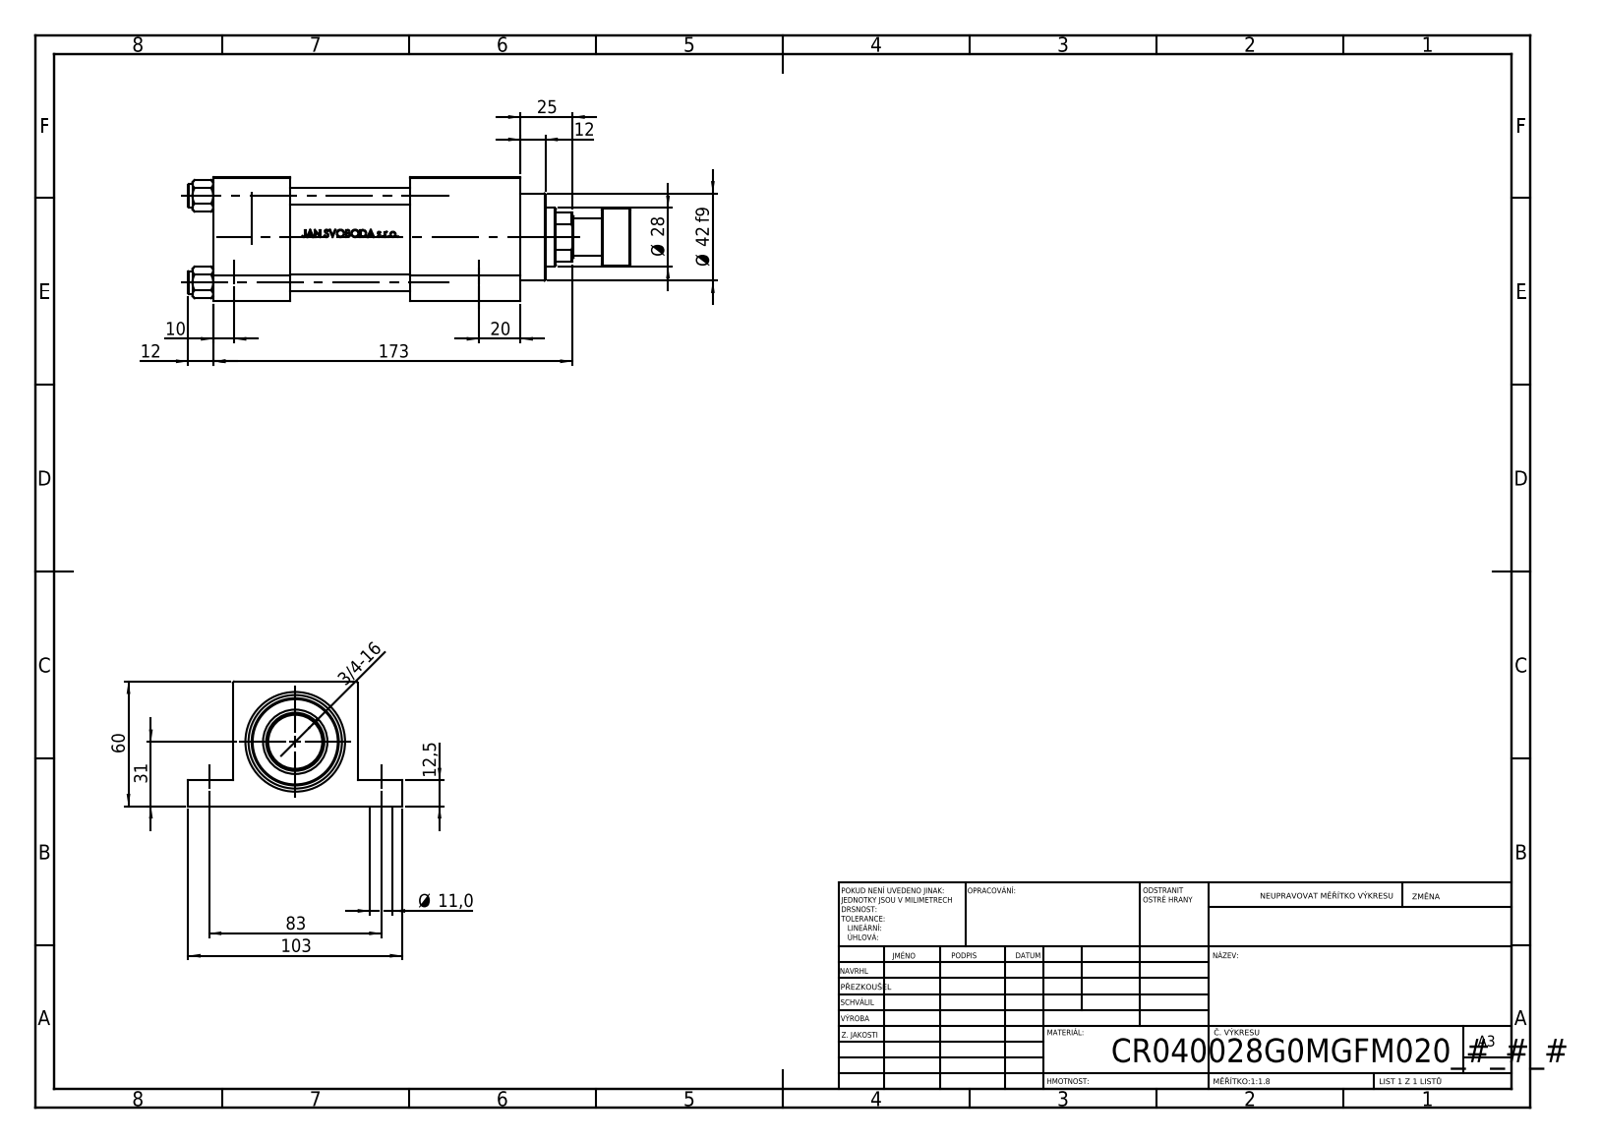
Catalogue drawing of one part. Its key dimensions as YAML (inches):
part_name: "V215CR_G_TYCINKA; V215_VC_A; V215CR_G_Body; V215CR_VCP_G (+2 more)"
step_written_by: "SolidWorks 2019 (CONFIG_CONTROL_DESIGN)"
units: inches
bodies: {solids: 12, faces: 1104, planar: 436, cylindrical: 130, other: 538}
overall_size: [8.386, 4.055, 2.362]
volume: 29.52
surface_area: 191.3
round_holes:
  - {diameter: 0.315, count: 4}
  - {diameter: 0.433, count: 4}
  - {diameter: 0.276, count: 2}
  - {diameter: 0.656, count: 2}
  - {diameter: 0.945, count: 2}
  - {diameter: 0.728, count: 1}
  - {diameter: 1.102, count: 1}
  - {diameter: 1.22, count: 1}
  - {diameter: 1.575, count: 1}
  - {diameter: 1.772, count: 1}
round_bosses_or_shafts:
  - {diameter: 0.433, count: 4}
  - {diameter: 1.811, count: 1}
  - {diameter: 1.654, count: 1}
  - {diameter: 1.063, count: 1}
  - {diameter: 0.709, count: 1}
face_to_face_distances: [2.362, 1.457, 0.492, 1.87, 2.087, 3.74, 2.283, 5.827, 4.37, 0.846]
hole_center_spacings: [1.642, 1.133, 1.189, 1.668, 1.766, 2.322, 3.268, 4.299]
